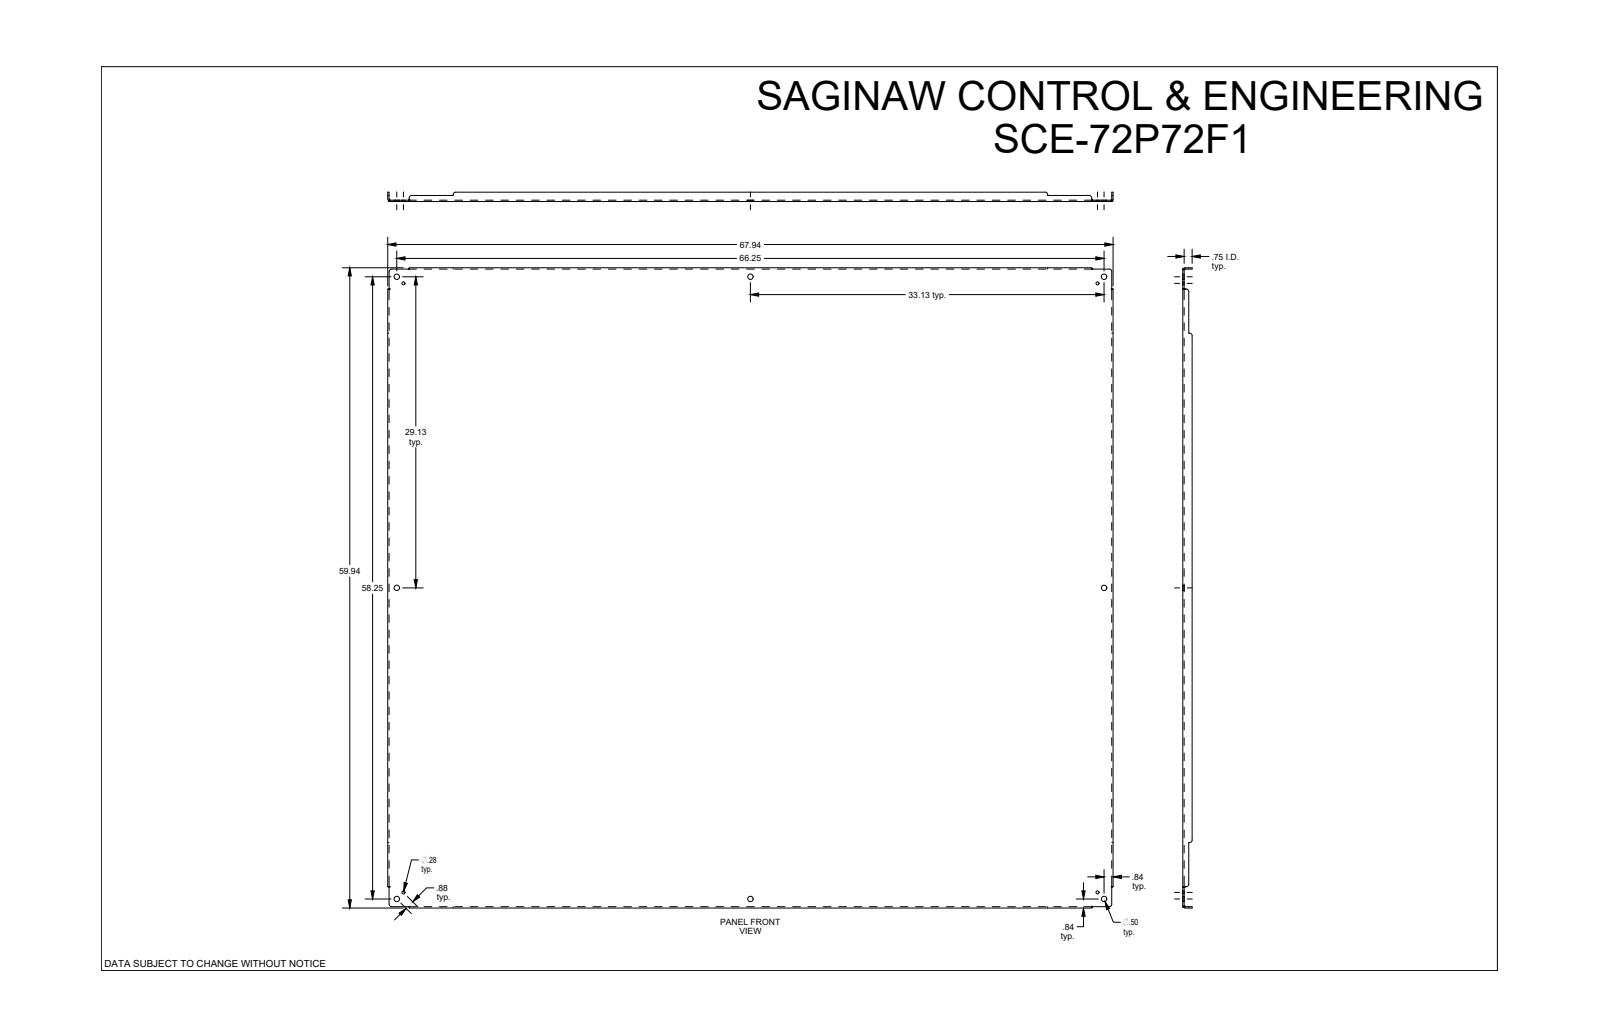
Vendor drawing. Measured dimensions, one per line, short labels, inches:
name: SCE-72P72F1
written by: SolidWorks 2019 (CONFIG_CONTROL_DESIGN)
unit: in
bodies: 1 solid, 110 faces (46 planar, 40 cylindrical, 24 other)
size: 67.938 × 59.938 × 0.875
volume: 527.4 in³; area: 8 473 in²
holes: 8× ⌀0.5, 4× ⌀0.281
rounds: 12× R0.25, 4× R0.112, 4× R0.237
face distances: 0.125, 0.125, 59.813, 67.813, 59.687, 59.938, 67.687, 67.938, 0.75, 0.875
hole spacings: 0.875, 28.513, 29.125, 32.512, 33.125, 44.108, 57.634, 65.634
